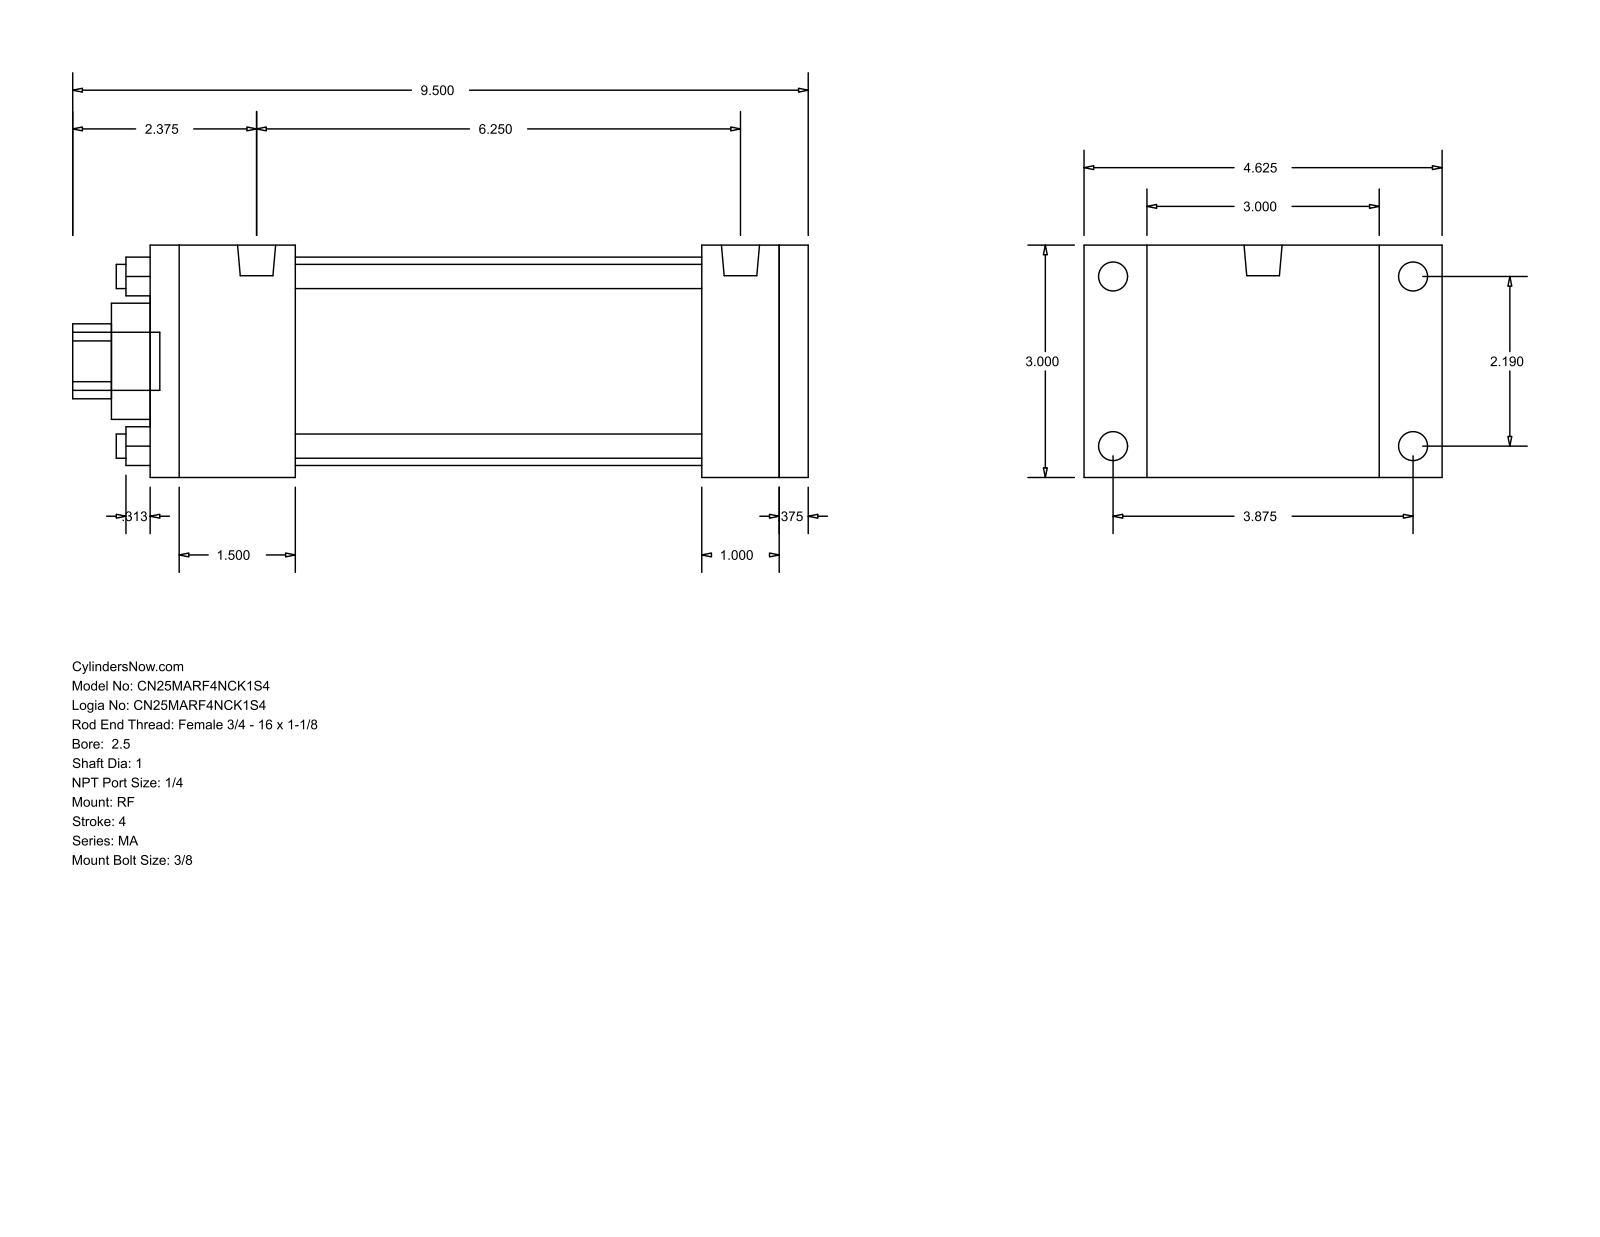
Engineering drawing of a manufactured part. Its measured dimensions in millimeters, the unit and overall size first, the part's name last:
Units: millimetres
Overall size (bounding box): 241.3 × 117.47 × 76.2
Round holes (diameter × count): ⌀7.94 ×4, ⌀25.4 ×1, ⌀38.1 ×1, ⌀68.33 ×1
Round bosses / shafts (diameter × count): ⌀9.53 ×4, ⌀7.94 ×4, ⌀12.49 ×2, ⌀19.05 ×1
Partial cylindrical surfaces — rounded edges, fillets, slot ends (radius × count): R12.29 ×1
Main face-to-face distances: 76.2, 215.9, 206.38, 9.52, 25.4, 47.63, 180.98, 133.35, 158.75, 168.27
Hole centre spacings: 39.33, 55.62, 78.66
Bodies: 0 solids, 92 faces (64 planar, 28 cylindrical, 0 other)
Part name (STEP PRODUCT): MA_RF__0250_1
STEP written by: GSSL Pune (CONFIG_CONTROL_DESIGN)
